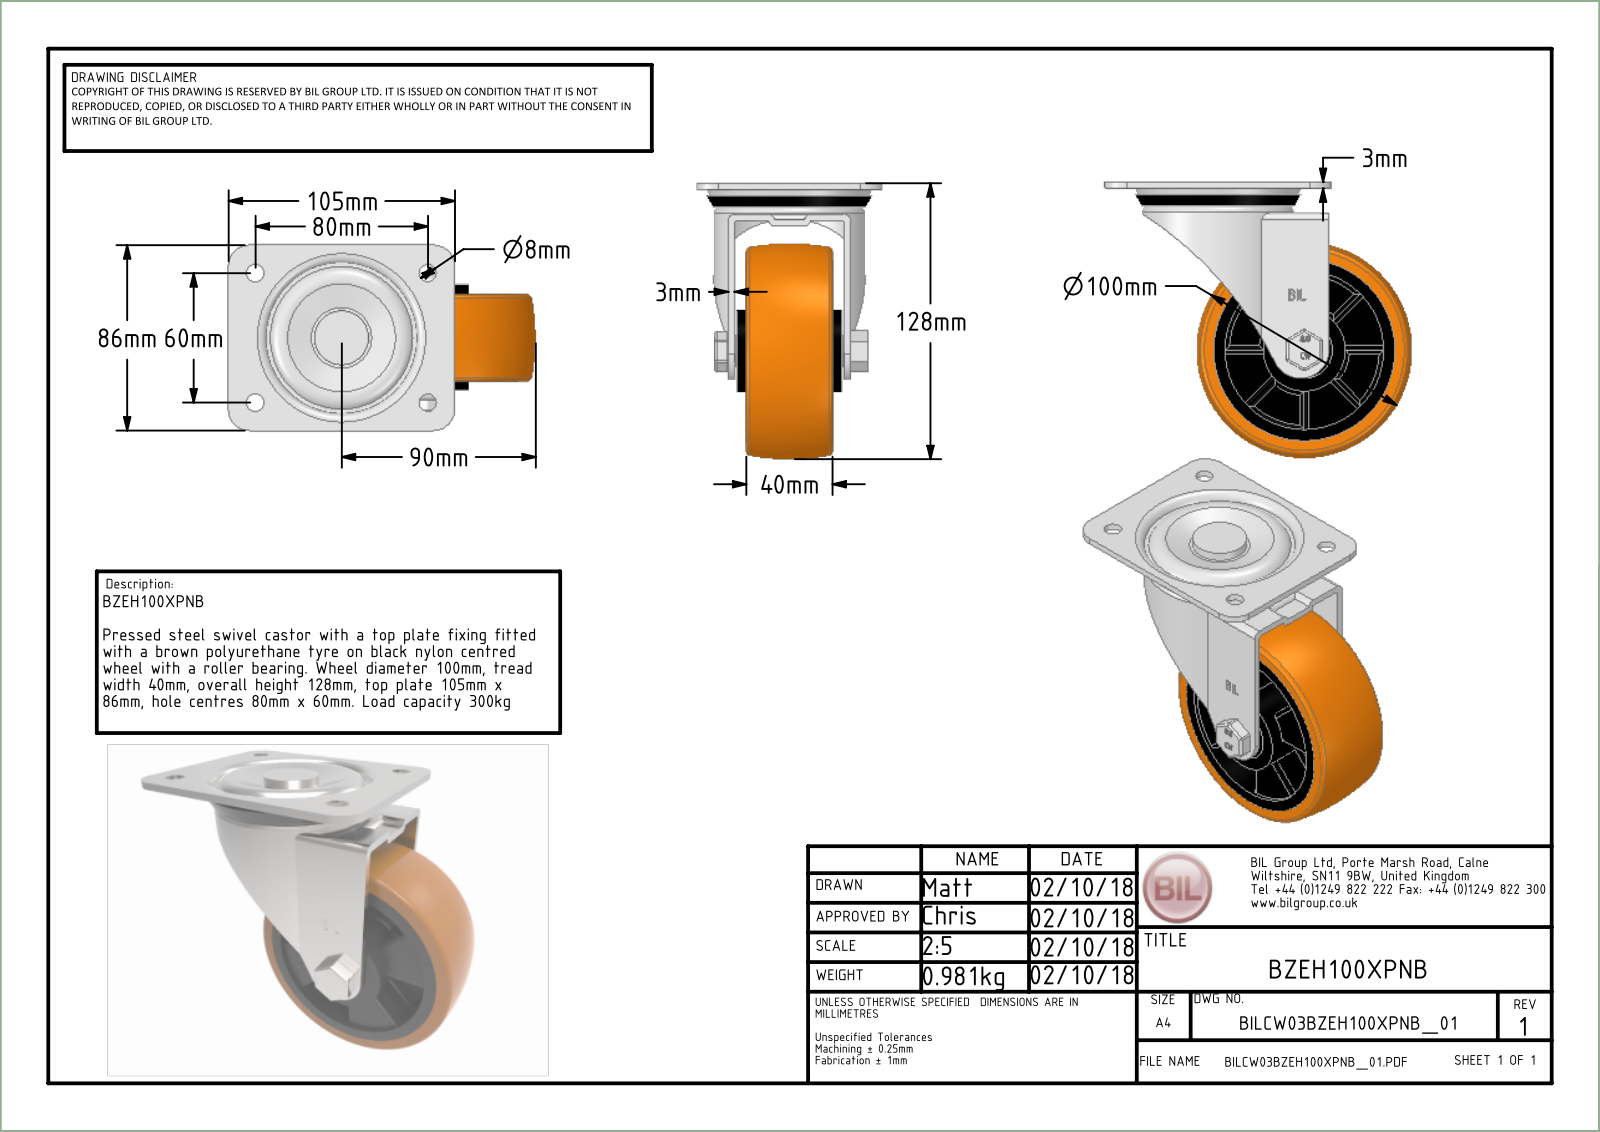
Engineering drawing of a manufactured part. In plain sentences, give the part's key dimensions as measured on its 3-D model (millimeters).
The part is named "BZEH100XPNB v3; BZEH100AS - 2 v2; ZINC PLATED, PRESSED STEEL TOP PLATE; ZINC PLATED, PRESSED STEEL TOP PLATE Geometry (+7 more)". Its 3-D file was written by "Autodesk Translation Framework v14.10.0.0 (AUTOMOTIVE_DESIGN)". It is 39 solids with 784 faces: 331 planar, 145 cylindrical and 308 other. Overall it measures 142.5 by 128 by 86 millimeters. Its volume is 316 080 cubic millimeters and its surface area 146 220 square millimeters. Round holes: 1 of diameter 10, 1 of diameter 10.2, 1 of diameter 10.5, 1 of diameter 12, 1 of diameter 15, 1 of diameter 15.5, 1 of diameter 26, 1 of diameter 27, 1 of diameter 30, 1 of diameter 64, 1 of diameter 73, 1 of diameter 85. Round bosses or shafts: 8 of diameter 4, 1 of diameter 70, 1 of diameter 54, 1 of diameter 37, 1 of diameter 26.9, 1 of diameter 25, 1 of diameter 22.5, 1 of diameter 21. Partial cylindrical surfaces (rounded edges, fillets, slot ends): 18 of radius 0.5, 8 of radius 4.5, 6 of radius 0.75, 4 of radius 10, 3 of radius 1.25, 2 of radius 3, 2 of radius 24.04, 1 of radius 9.25. The main face-to-face distances are 3, 5, 10, 2, 4, 8, 5.5, 7, 8.5, 48.5.
